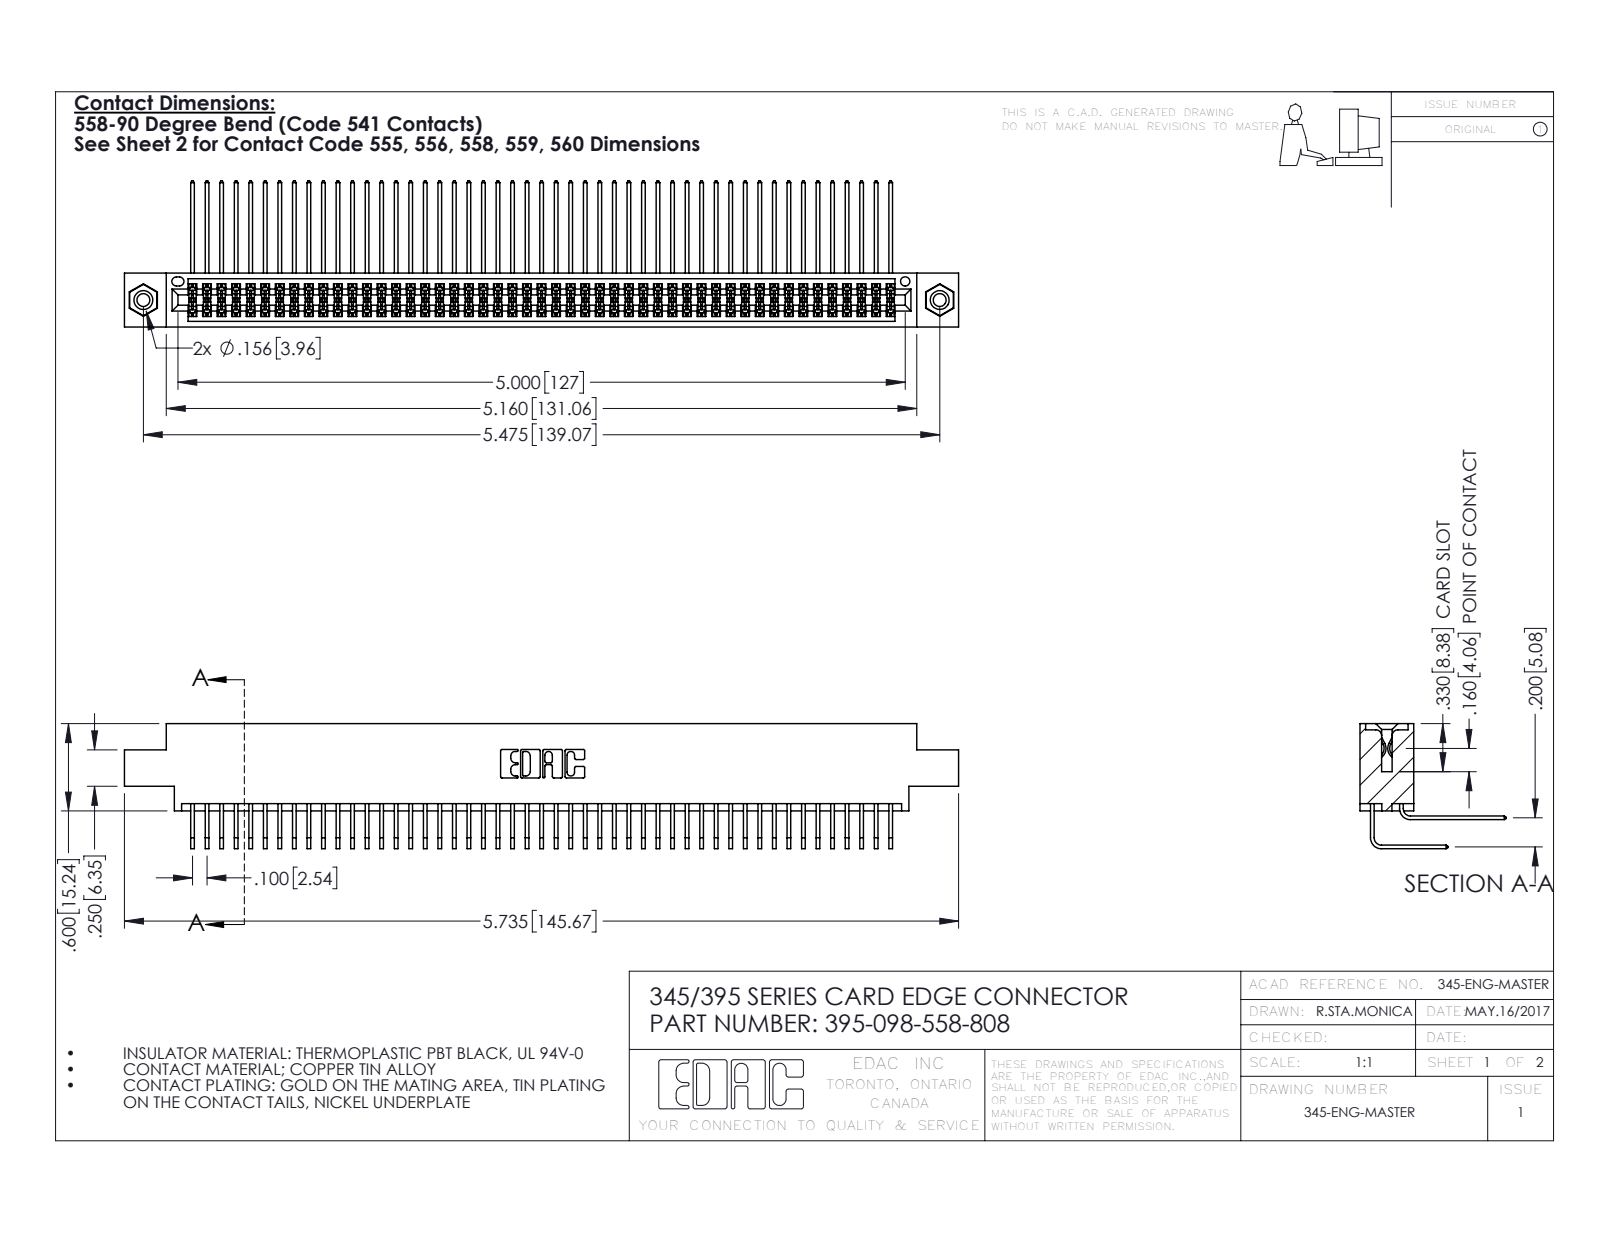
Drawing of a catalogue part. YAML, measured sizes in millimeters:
part_name: "345-250-001_345-250-003-102; 345 Part_0.170 Offset - 0.156 Dia-TI; 345-292-001_558 559 Tail - 1; 395-098-558-808 (+1 more)"
step_written_by: "SolidWorks 2016 (CONFIG_CONTROL_DESIGN)"
units: millimeters
bodies: {solids: 101, faces: 5286, planar: 3546, cylindrical: 1724, other: 16}
overall_size: [145.7, 25.5, 21.8]
volume: 14700
surface_area: 24620
round_holes:
  - {diameter: 2.3, count: 2}
  - {diameter: 3.2, count: 2}
  - {diameter: 4, count: 2}
  - {diameter: 1.6, count: 1}
round_bosses_or_shafts:
  - {diameter: 3.9, count: 2}
partial_cylinders:
  - {radius: 0.2, count: 148}
  - {radius: 0.3, count: 22}
  - {radius: 0.2, count: 6}
  - {radius: 0.8, count: 6}
  - {radius: 0.7, count: 3}
  - {radius: 0.4, count: 2}
  - {radius: 0.5, count: 2}
  - {radius: 0.6, count: 2}
face_to_face_distances: [1.8, 7.6, 5.1, 9.4, 2.5, 6.9, 0.6, 5.7, 4.4, 0.6]
hole_center_spacings: [6.9, 133.1, 139.1]
